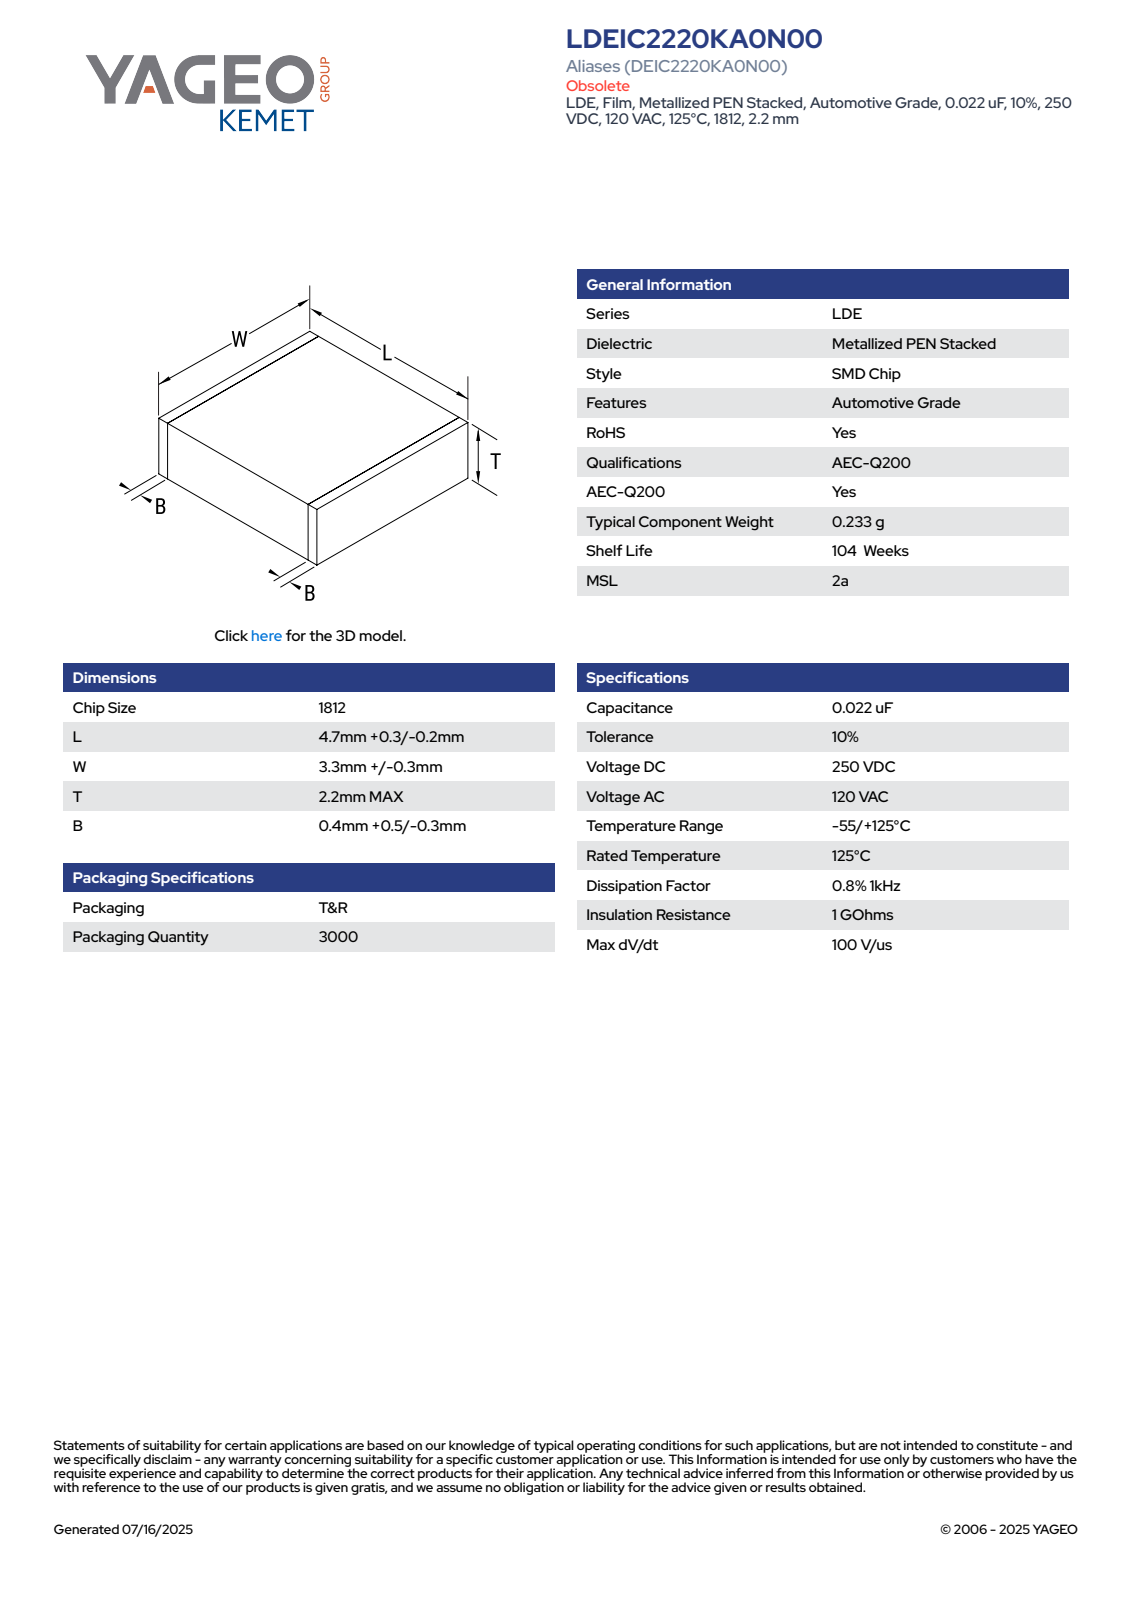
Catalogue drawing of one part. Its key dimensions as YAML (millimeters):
part_name: "CFS_LDELDB_1812_L5W3.6T2.2B0.9"
step_written_by: "SolidWorks 2020 (AUTOMOTIVE_DESIGN)"
units: millimeters
bodies: {solids: 4, faces: 73, planar: 73, cylindrical: 0, other: 0}
overall_size: [5, 3.6, 2.2]
volume: 39
surface_area: 75
face_to_face_distances: [2.18, 3.58, 5, 2.19, 3.59, 2.2, 3.6, 0.5, 4.5, 4]
